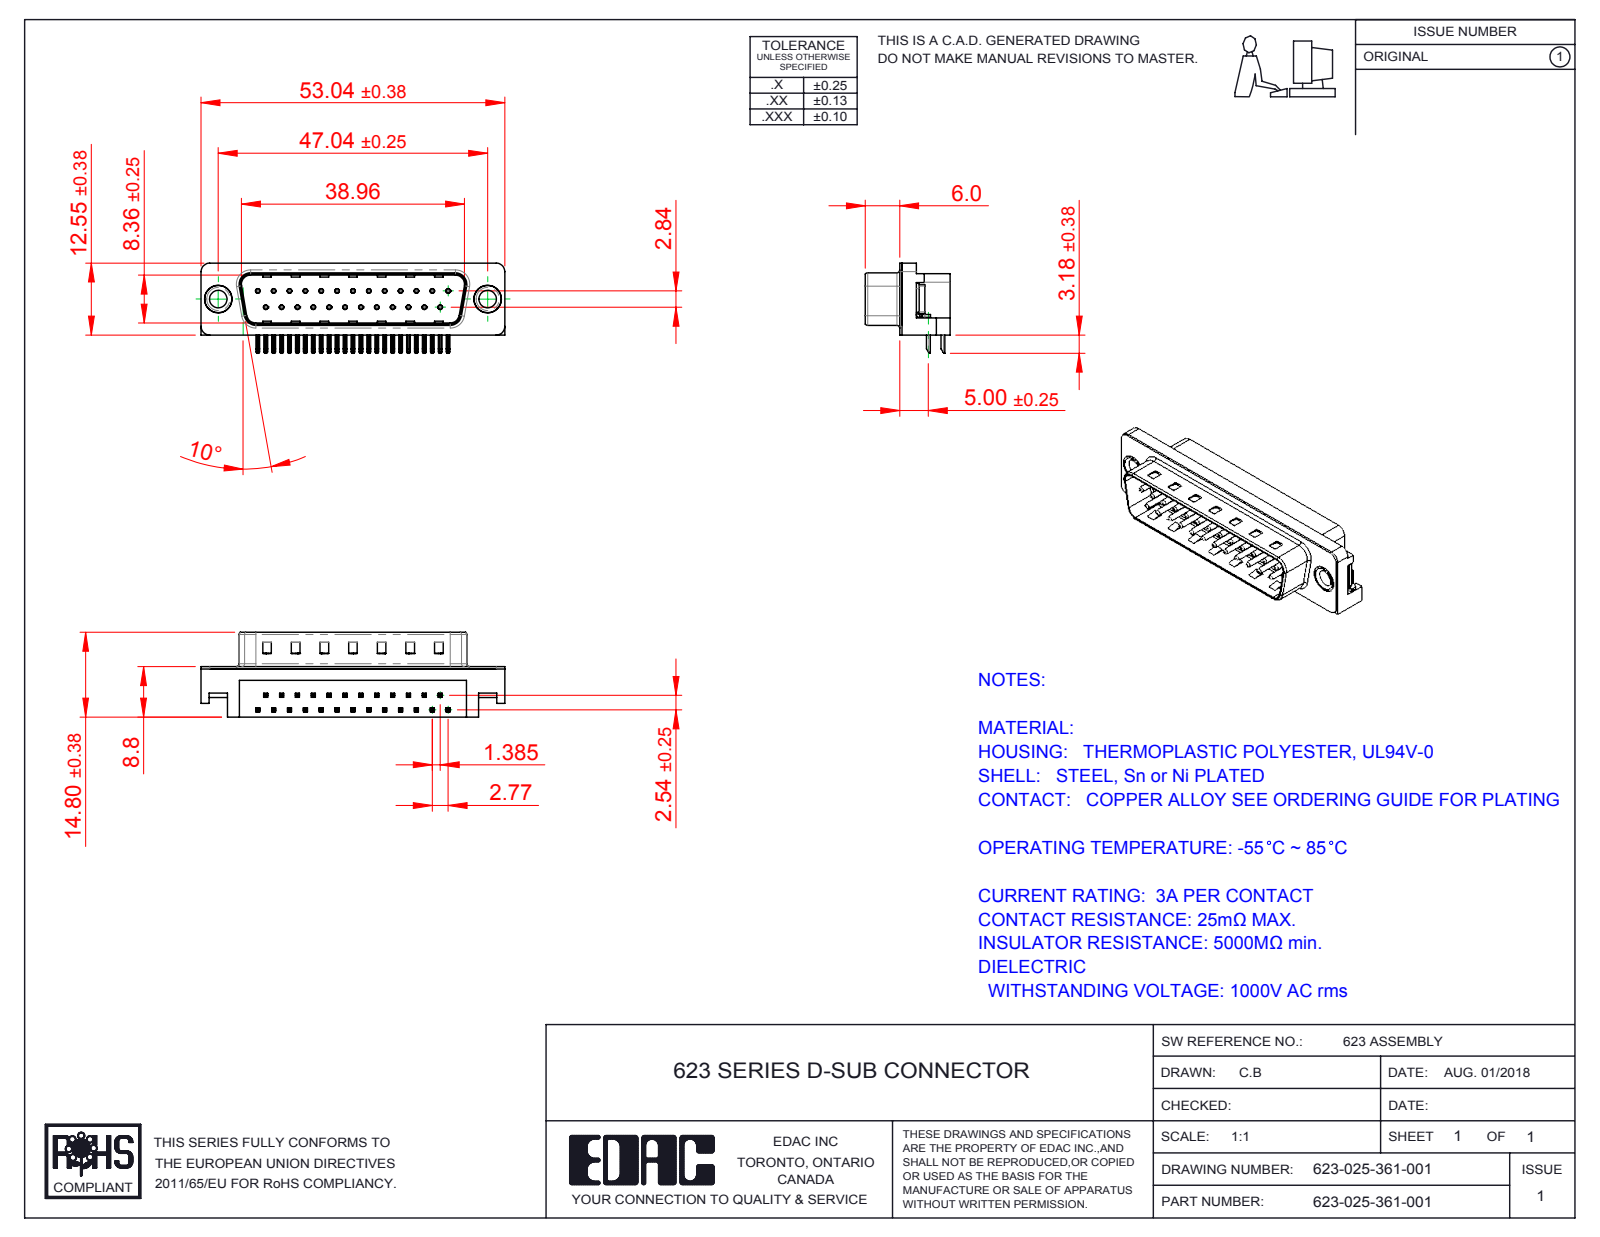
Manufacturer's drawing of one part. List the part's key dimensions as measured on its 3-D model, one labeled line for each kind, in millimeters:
Part name (STEP PRODUCT): 623 Contact Top; 623 Shell_25 Socket; 623-025-361-001; 623 Thru Hole Rivet (+3 more)
STEP written by: SolidWorks 2016 (CONFIG_CONTROL_DESIGN)
Units: millimetres
Bodies: 31 solids, 2213 faces (1405 planar, 631 cylindrical, 177 other)
Overall size (bounding box): 53.04 × 15.73 × 14.8
Volume: 4 712 mm³ · Surface area: 6 693 mm²
Round holes (diameter × count): ⌀0.35 ×25, ⌀0.8 ×25, ⌀3.05 ×2, ⌀4 ×2, ⌀4.8 ×2, ⌀5 ×2
Round bosses / shafts (diameter × count): ⌀0.75 ×25, ⌀4.9 ×2, ⌀4.75 ×2, ⌀3.85 ×2
Partial cylindrical surfaces — rounded edges, fillets, slot ends (radius × count): R0.25 ×108, R0.12 ×50, R1 ×16, R0.5 ×9, R1.5 ×7, R0.9 ×4, R1.6 ×4, R2 ×4
Main face-to-face distances: 0.4, 8.4, 2.1, 1.7, 8.76, 10.46, 10.86, 10.35, 8.8, 5.9
Hole centre spacings: 3.16, 2.77, 11.08, 5.54, 8.31, 5.03, 13.85, 7.48
